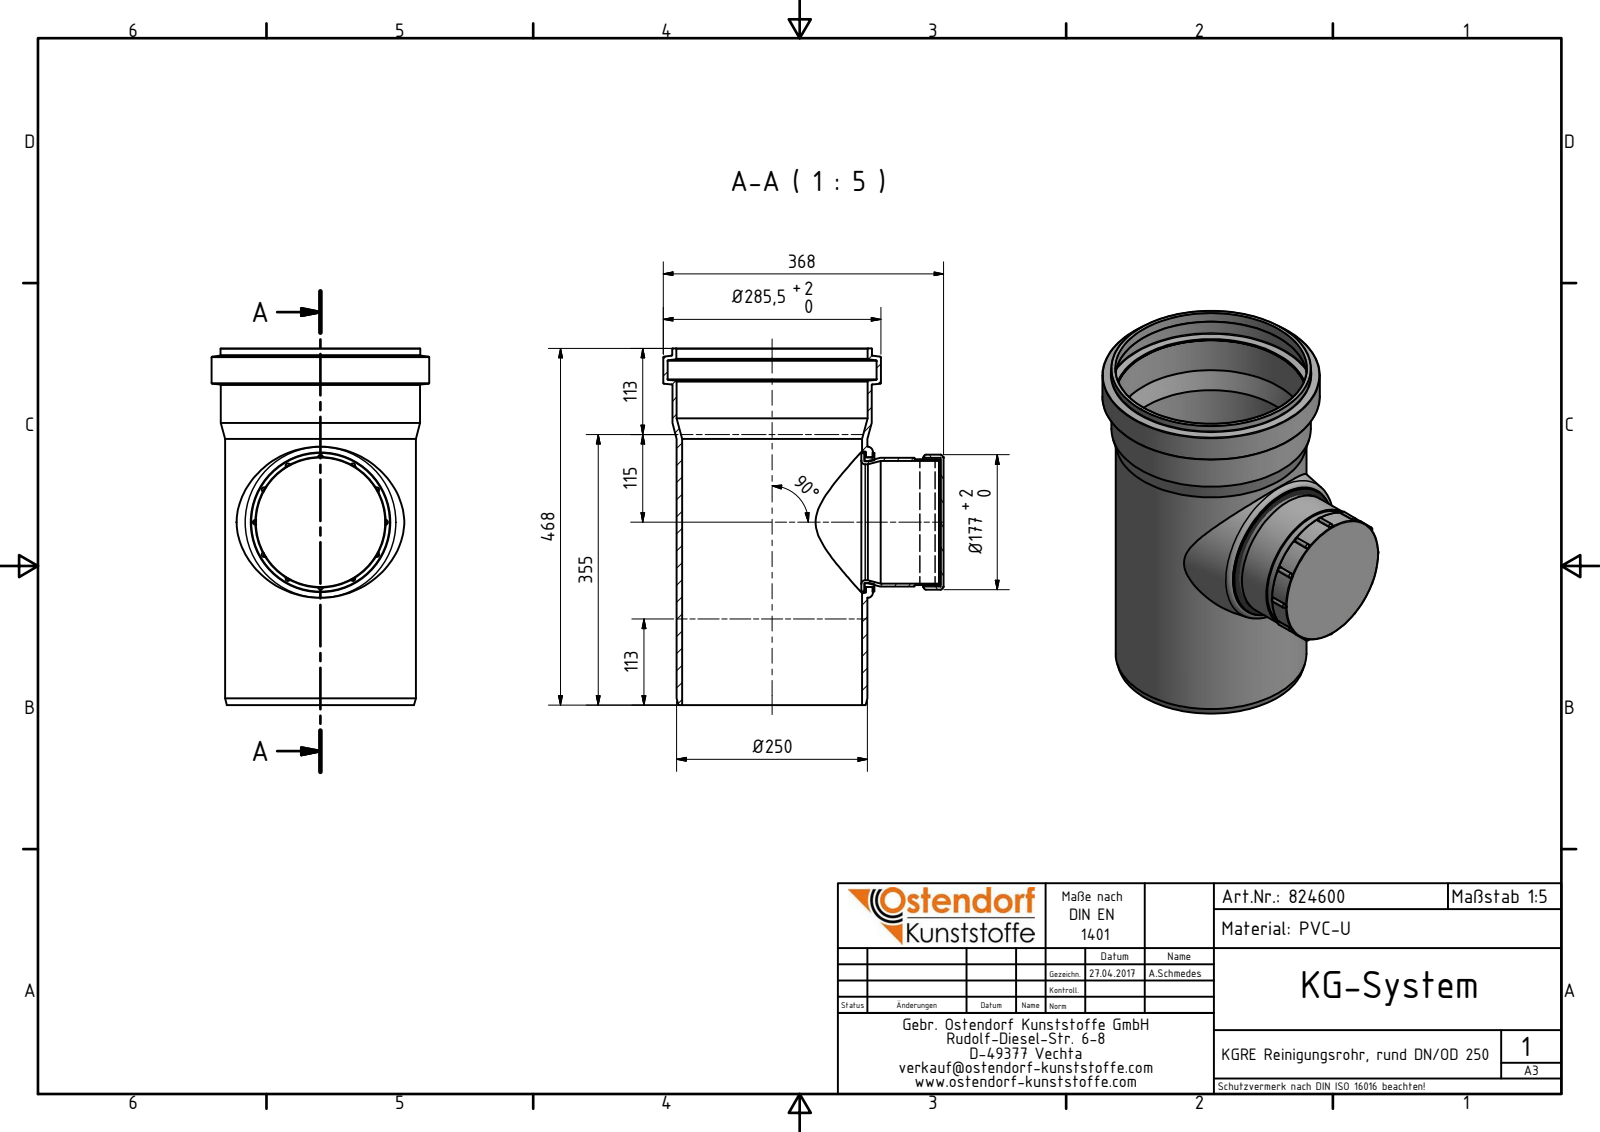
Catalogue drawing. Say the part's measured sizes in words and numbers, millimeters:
The part is named "824600 KGRE Reinigungsrohr, rund DN_OD 250; 824600 KGRE Reinigungsrohr, rund DN_OD 250 Dichtung; 824600 KGRE Reinigungsrohr, rund DN_OD 250 Abzweig; 824600 KGRE Reinigungsrohr, rund DN_OD 250 Deckel". Its 3-D file was written by "Autodesk Inventor 2016 (AUTOMOTIVE_DESIGN)". It is 4 solids with 207 faces: 64 planar, 92 cylindrical and 51 other. Overall it measures 468 by 368 by 285.5 millimeters. Its volume is 2 863 000 cubic millimeters and its surface area 978 713 square millimeters. Round holes: 1 of diameter 152, 1 of diameter 160, 1 of diameter 161, 1 of diameter 165, 1 of diameter 170, 1 of diameter 236.3, 1 of diameter 250.8, 1 of diameter 251.1, 1 of diameter 274.5. Round bosses or shafts: 1 of diameter 285.5, 1 of diameter 262.1, 1 of diameter 261.8, 1 of diameter 250.5, 1 of diameter 182, 1 of diameter 171, 1 of diameter 169. Partial cylindrical surfaces (rounded edges, fillets, slot ends): 36 of radius 2.95, 12 of radius 3. The main face-to-face distances are 4, 104, 2, 11, 100, 102, 98, 93, 89, 9.
